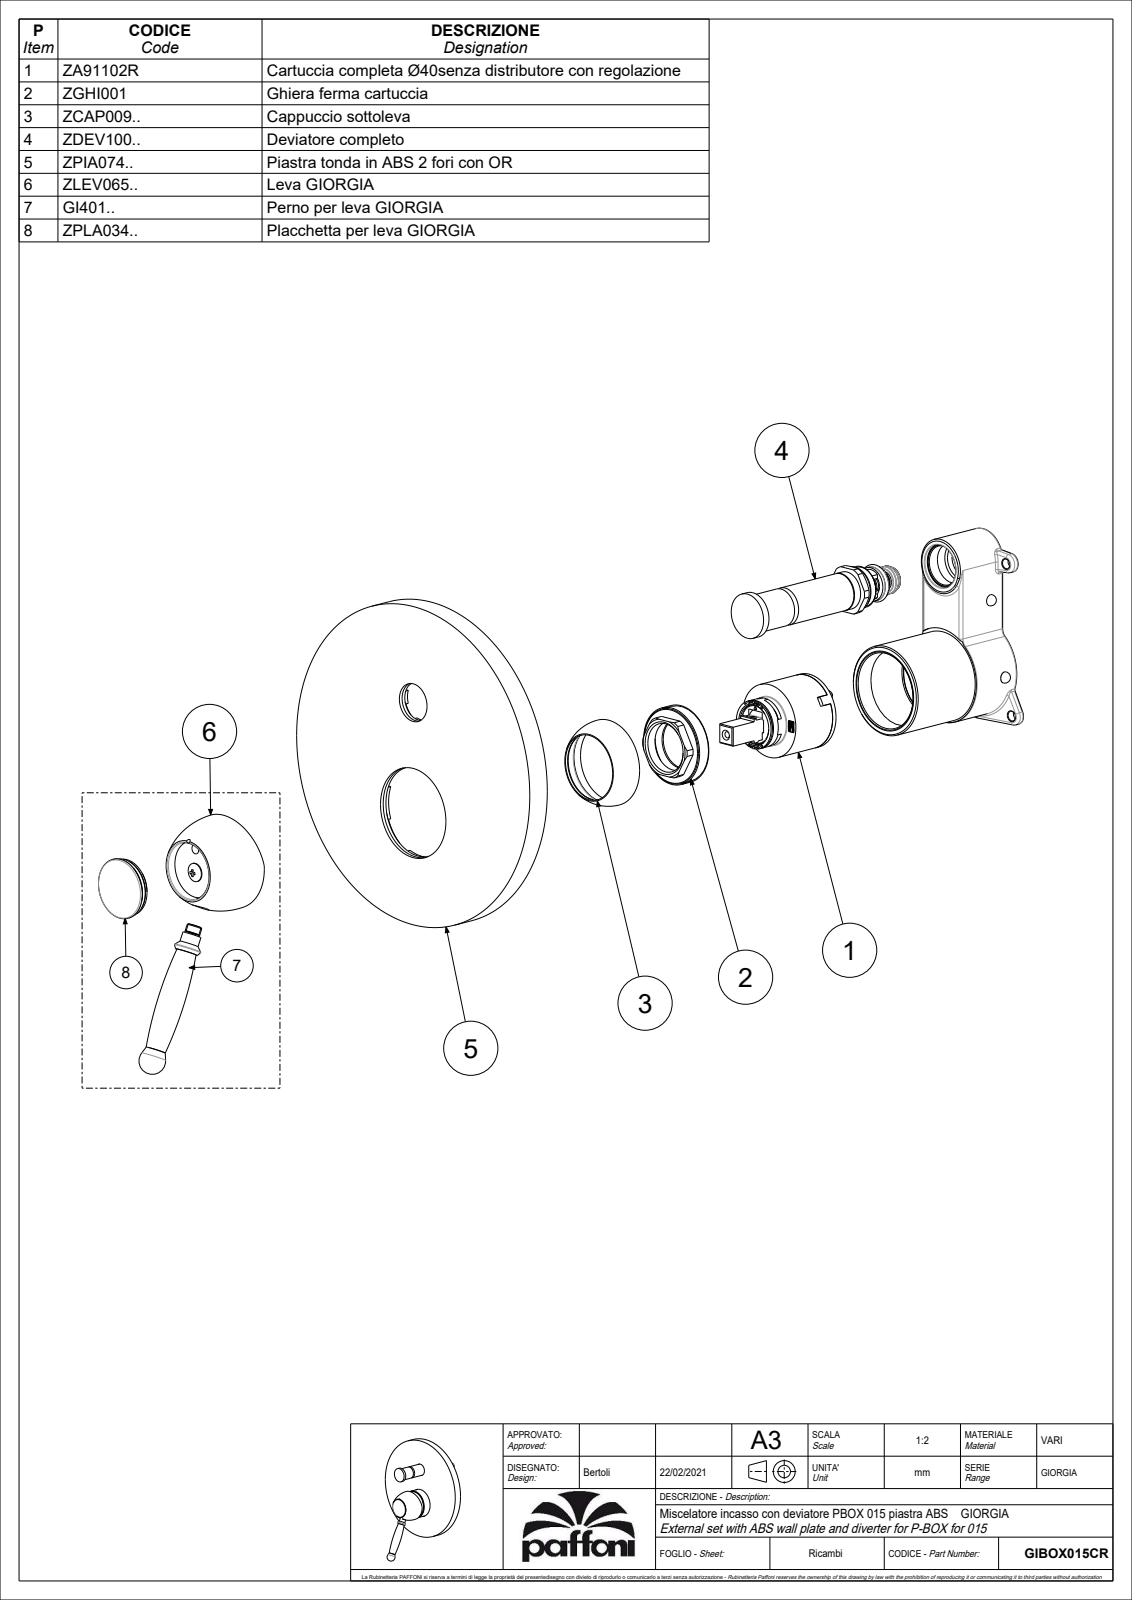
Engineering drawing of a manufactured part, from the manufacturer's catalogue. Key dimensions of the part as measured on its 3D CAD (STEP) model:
Part name (STEP PRODUCT): GIBOX015CR
STEP written by: CREO PARAMETRIC BY PTC INC, 2020044 (CONFIG_CONTROL_DESIGN)
Units: millimetres
Bodies: 8 solids, 1045 faces (613 planar, 267 cylindrical, 165 other)
Overall size (bounding box): 203.74 × 173 × 92.28
Volume: 252 566 mm³ · Surface area: 126 742 mm²
Round holes (diameter × count): ⌀5 ×3, ⌀3 ×1, ⌀3.3 ×1, ⌀4 ×1, ⌀7.1 ×1, ⌀12 ×1, ⌀16 ×1, ⌀18.2 ×1, ⌀20.5 ×1, ⌀21 ×1, ⌀21.2 ×1, ⌀25 ×1
Round bosses / shafts (diameter × count): ⌀173 ×1, ⌀167 ×1, ⌀57 ×1, ⌀48.1 ×1, ⌀39.5 ×1, ⌀33 ×1, ⌀32 ×1, ⌀29.9 ×1
Partial cylindrical surfaces — rounded edges, fillets, slot ends (radius × count): R0.5 ×26, R0.2 ×24, R2 ×1, R3.5 ×1, R6.5 ×1, R7 ×1, R10.05 ×1, R10.75 ×1
Main face-to-face distances: 13, 11, 2, 6.5, 21, 8, 10, 4.5, 42, 34
Hole centre spacings: 1.6, 1.62, 10.98, 11, 12.6, 14.77, 25.75, 25.77
